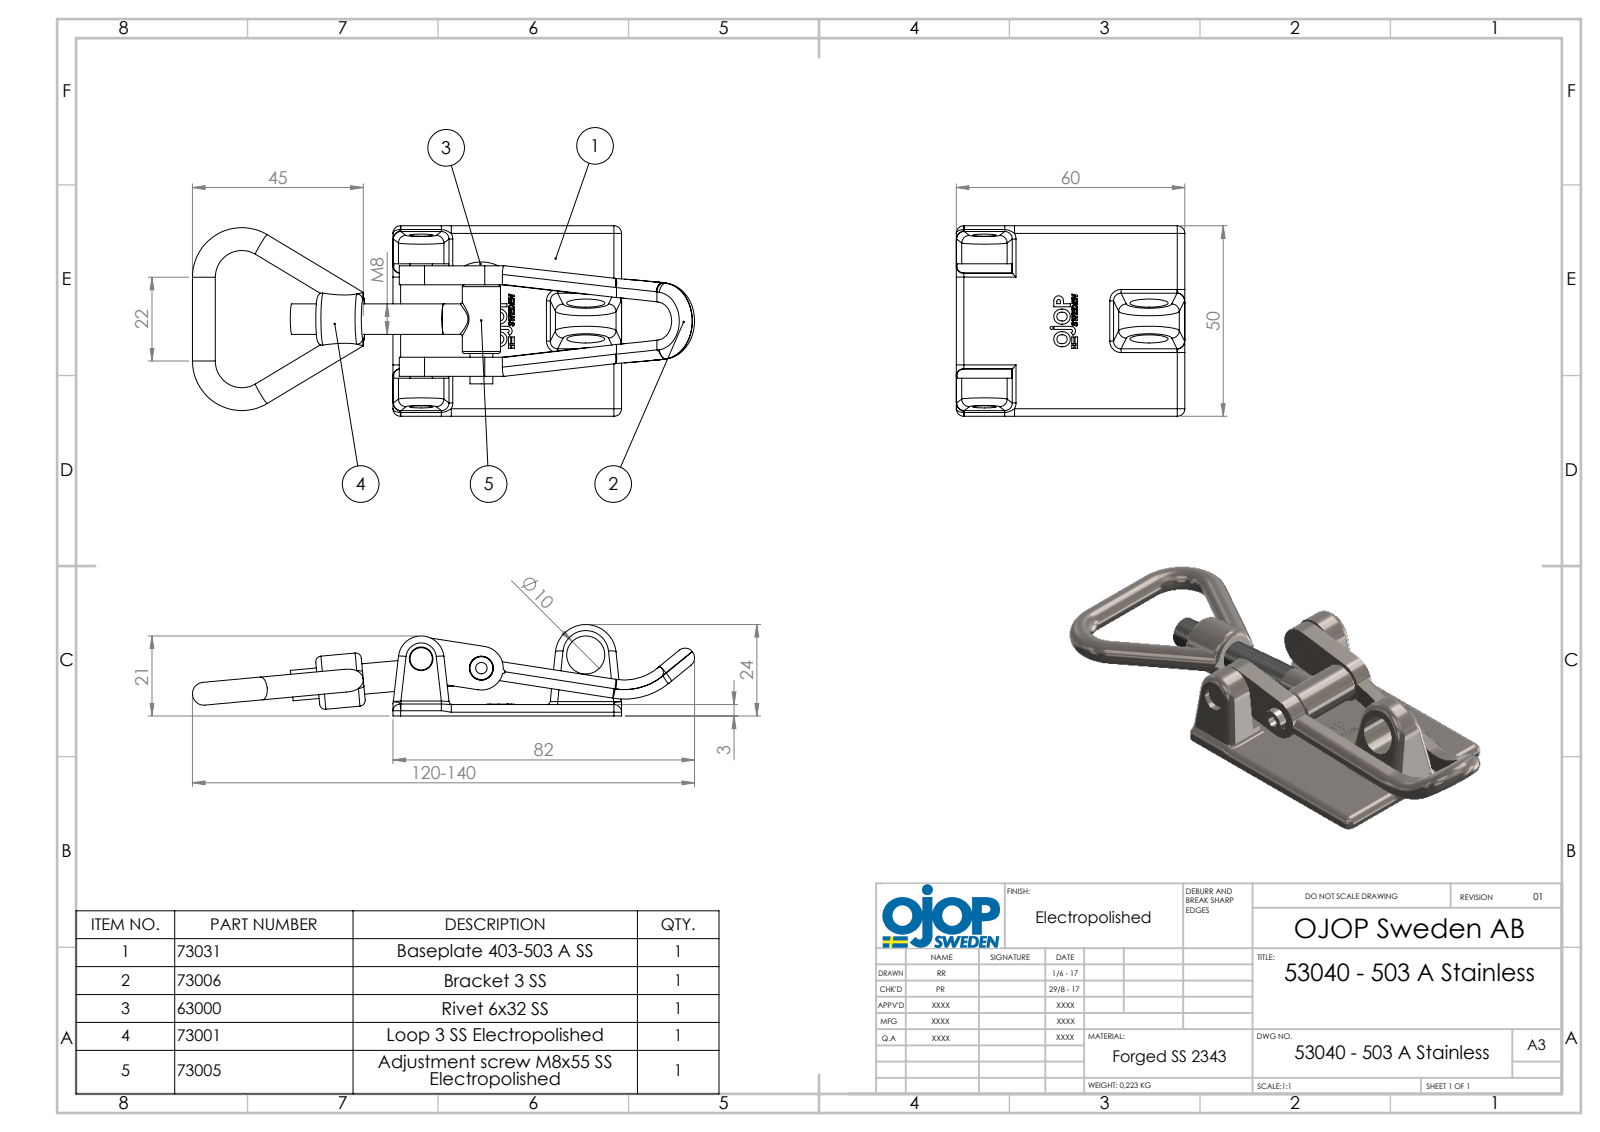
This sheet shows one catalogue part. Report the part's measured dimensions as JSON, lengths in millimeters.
{"part_name": "bygel 3; Hålnit 6x32; Ring 3; Justerskruv M8 (+2 more)", "step_written_by": "SolidWorks 2015 (AUTOMOTIVE_DESIGN)", "units": "millimeters", "bodies": {"solids": 5, "faces": 254, "planar": 60, "cylindrical": 97, "other": 97}, "overall_size": [138.31, 50, 24], "volume_mm3": 28961, "surface_area_mm2": 18970, "round_holes": [[6.2, 2], [3, 1], [6.3, 1], [8.1, 1], [10, 1]], "round_bosses_or_shafts": [[6, 4], [10, 1], [8.01, 1], [8, 1], [5.85, 1]], "partial_cylinders_radius": [[2, 30], [2.5, 8], [6.99, 4], [1.5, 2], [6.15, 2], [2.4, 1], [5, 1], [6, 1]], "face_to_face_distances": [3, 5, 25, 30, 20, 3.65, 8.65, 10, 15, 35], "hole_center_spacings": [16.01, 27.39, 43.21]}
